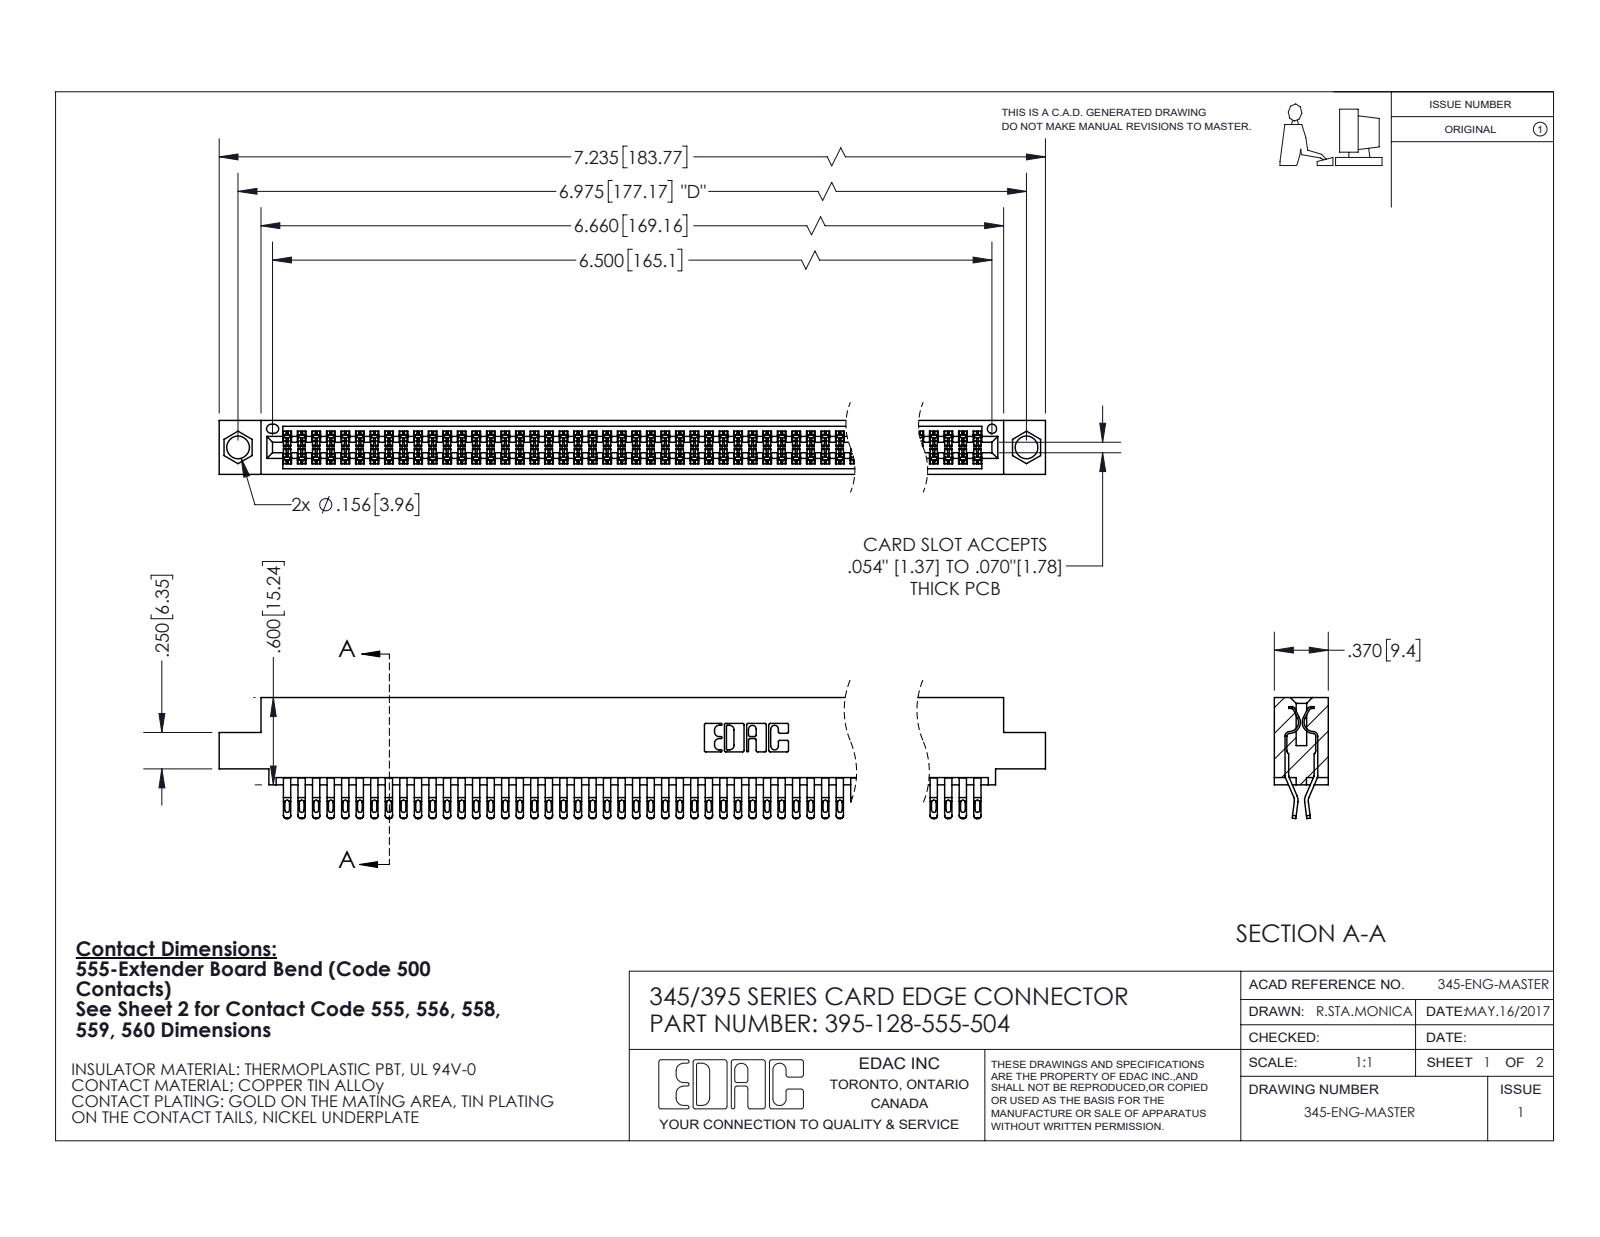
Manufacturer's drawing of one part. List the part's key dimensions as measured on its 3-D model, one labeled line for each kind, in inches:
Part name (STEP PRODUCT): 395-128-555-504; 345-292-001_555 Tail; 345 Part_0.110 Offset - 0.156 Dia-TI
STEP written by: SolidWorks 2020 (CONFIG_CONTROL_DESIGN)
Units: inches
Bodies: 129 solids, 7312 faces (4066 planar, 3246 cylindrical, 0 other)
Overall size (bounding box): 7.235 × 0.832 × 0.37
Volume: 1.114 in³ · Surface area: 44.38 in²
Round holes (diameter × count): ⌀0.156 ×2, ⌀0.064 ×1
Partial cylindrical surfaces — rounded edges, fillets, slot ends (radius × count): R0.016 ×320, R0.006 ×256, R0.02 ×256, R0.01 ×22, R0.007 ×6, R0.031 ×6, R0.026 ×3, R0.01 ×2
Main face-to-face distances: 0.298, 0.072, 0.025, 0.37, 0.2, 0.098, 0.272, 0.225, 0.175, 0.149
Hole centre spacings: 0.27, 6.739, 6.975
